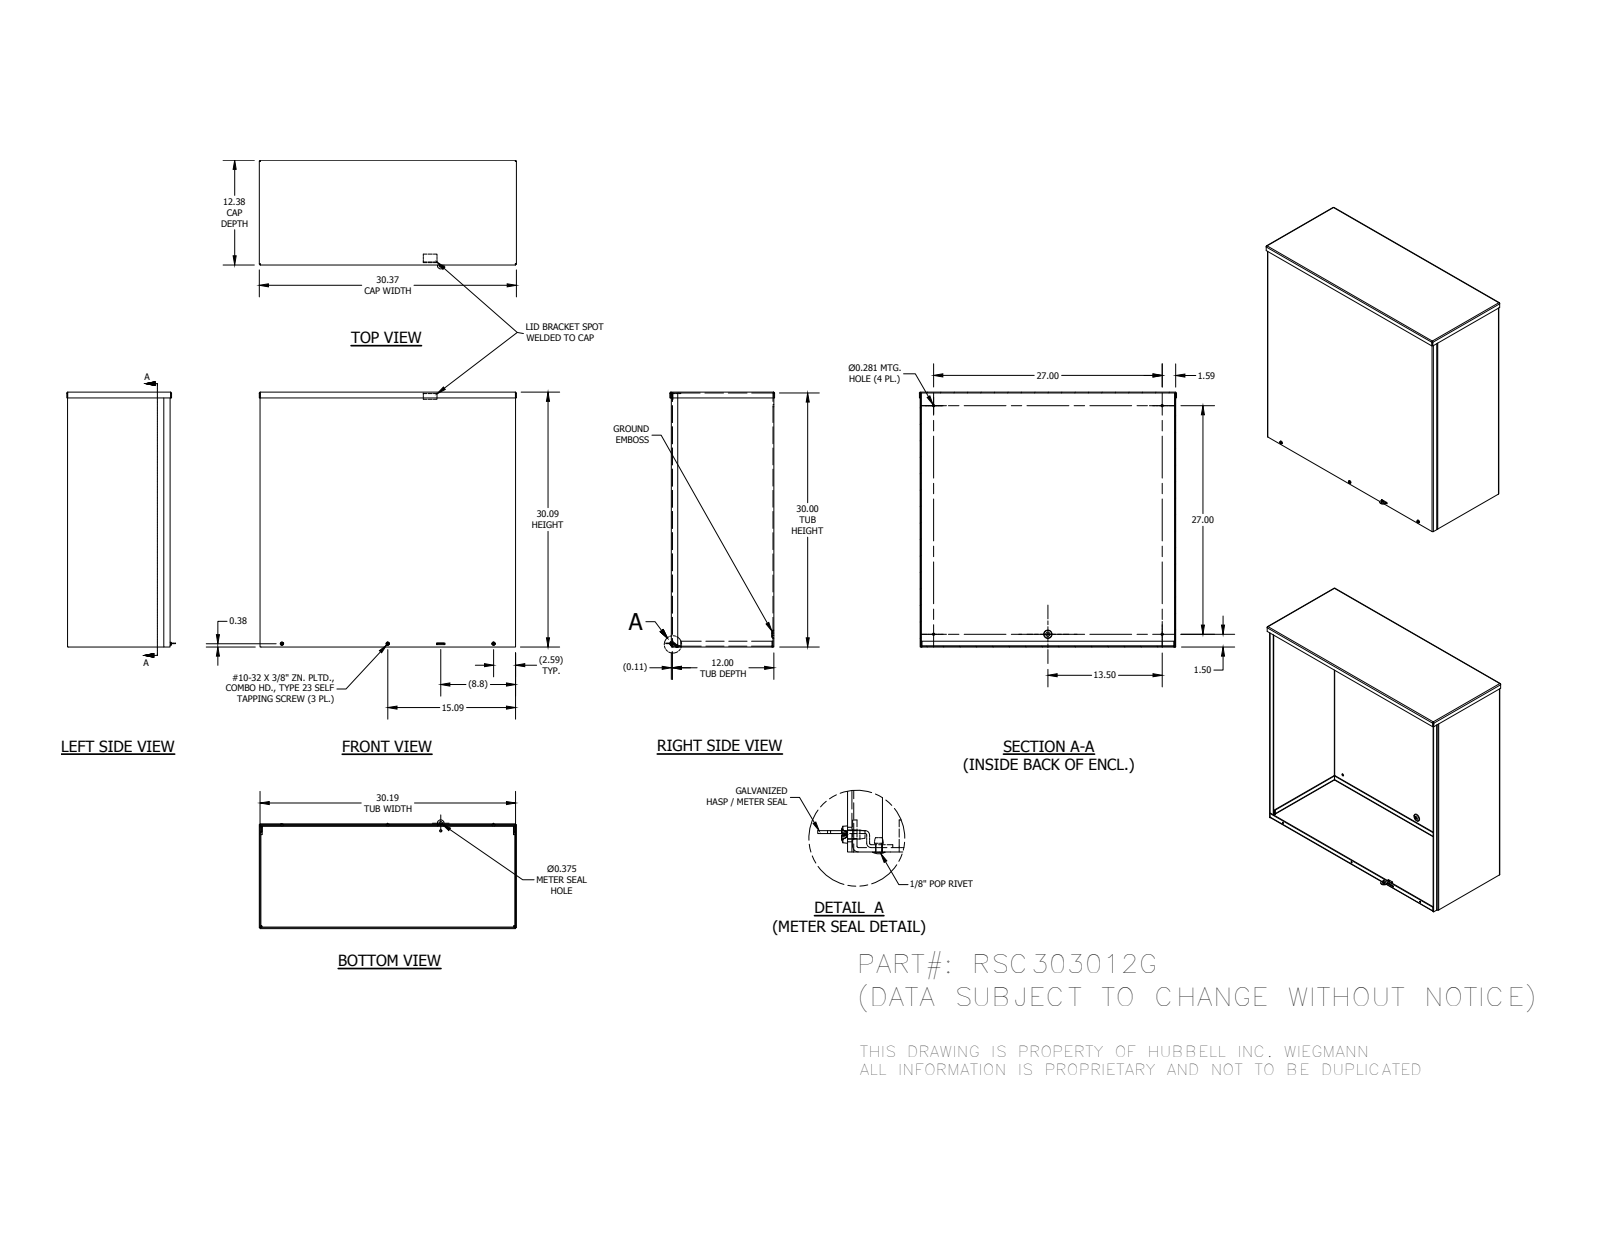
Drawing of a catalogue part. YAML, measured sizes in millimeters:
part_name: "RSC303012GBKPA; RSC3012GEWPA; RSC3030GLFA; RSC3012GCPA (+5 more)"
step_written_by: "Autodesk Inventor 2014 (AUTOMOTIVE_DESIGN)"
units: millimeters
bodies: {solids: 11, faces: 367, planar: 226, cylindrical: 64, other: 77}
overall_size: [771.52, 765.4, 326.24]
volume: 5210000
surface_area: 4411000
round_holes:
  - {diameter: 7.94, count: 6}
  - {diameter: 4.34, count: 4}
  - {diameter: 7.14, count: 4}
  - {diameter: 3.17, count: 1}
  - {diameter: 3.45, count: 1}
  - {diameter: 9.52, count: 1}
round_bosses_or_shafts:
  - {diameter: 4.83, count: 3}
  - {diameter: 6.65, count: 1}
  - {diameter: 3.17, count: 1}
partial_cylinders:
  - {radius: 0.79, count: 19}
  - {radius: 3.17, count: 16}
  - {radius: 2.37, count: 2}
  - {radius: 2.67, count: 1}
  - {radius: 10.16, count: 1}
face_to_face_distances: [2.38, 305.2, 764.38, 762, 307.58, 302.82, 766.76, 759.62, 760.59, 3.79]
hole_center_spacings: [317.5, 344.09, 661.02, 685.8, 792.4, 807.95, 38.24, 318.78]
